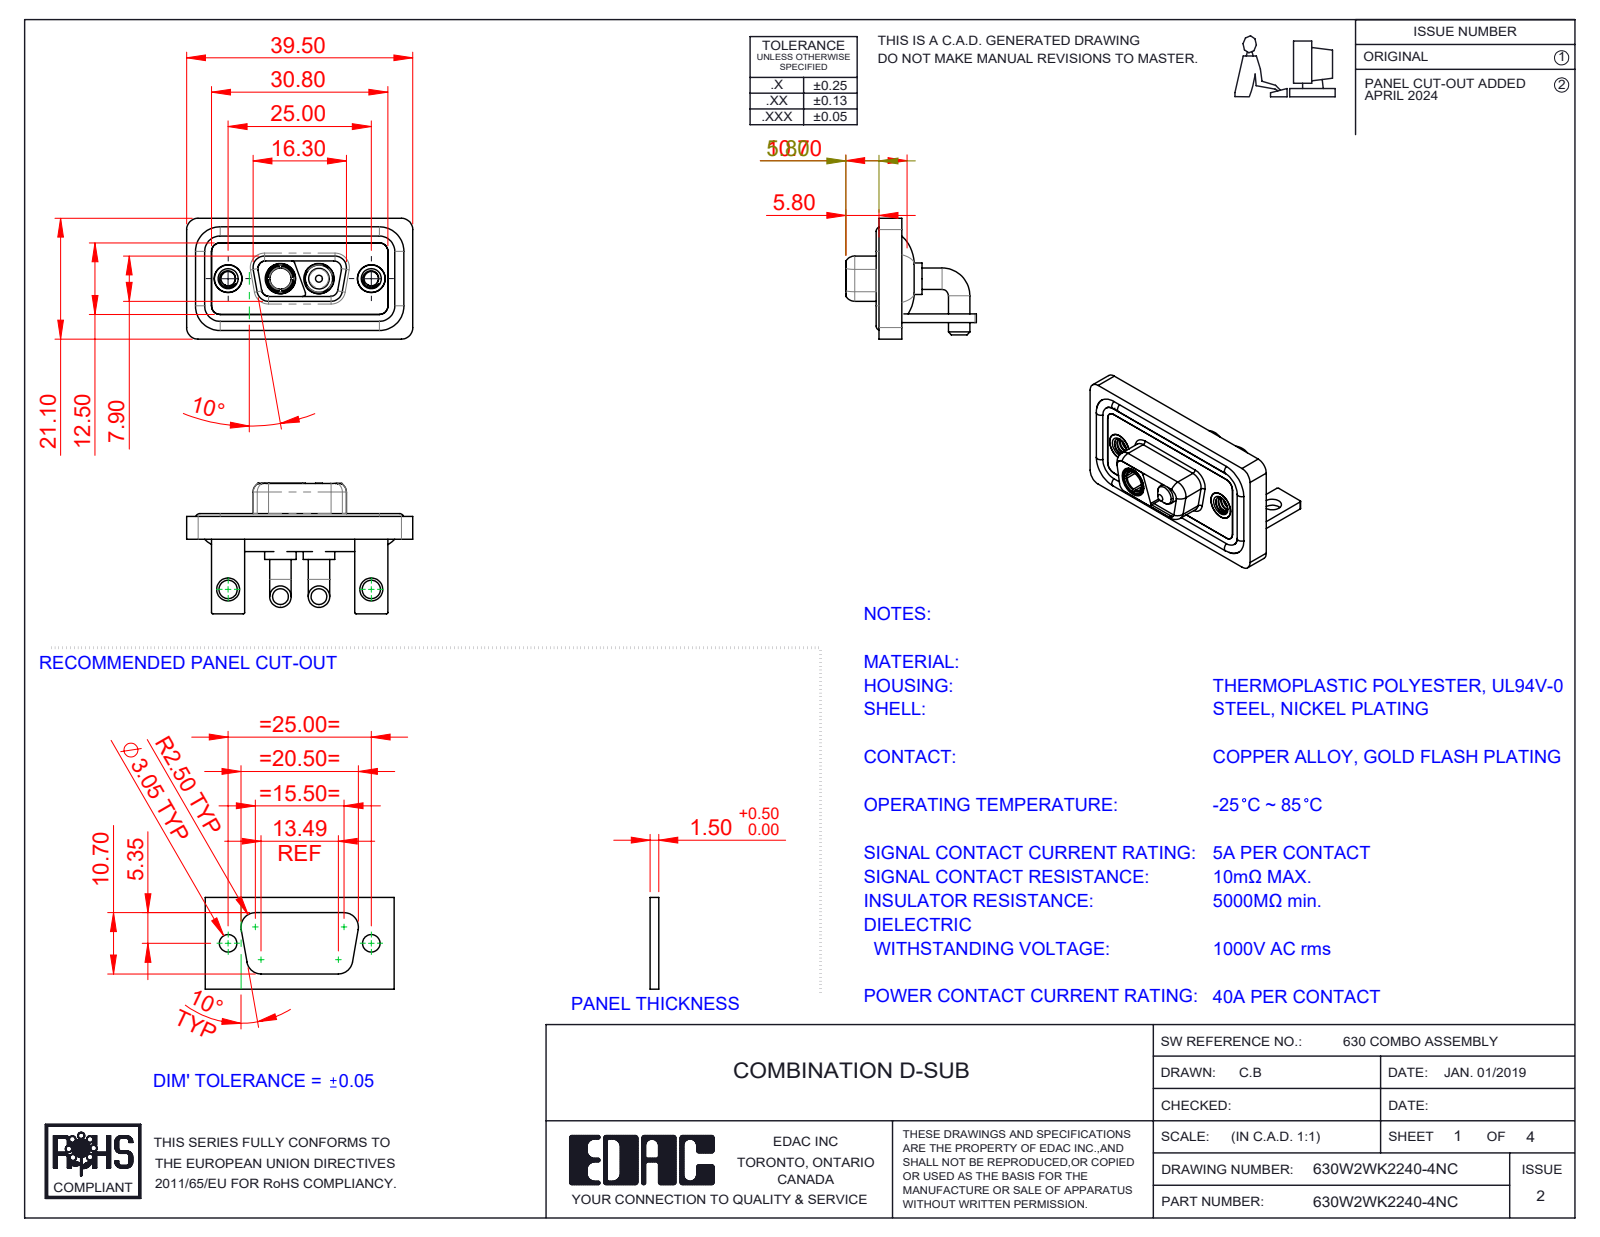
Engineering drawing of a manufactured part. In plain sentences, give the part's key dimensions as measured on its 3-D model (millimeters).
The part is named "Power Pin_40A RA; 630Combo Waterproof Housing_09 Contacts; 630Combo Stabilizer Bracket_50 Contacts; Power Socket_40A RA (+5 more)". Its 3-D file was written by "SolidWorks 2023 (CONFIG_CONTROL_DESIGN)". It is 13 solids with 550 faces: 164 planar, 257 cylindrical and 129 other. Overall it measures 39.5 by 22.8 by 21.1 millimeters. Its volume is 5 212 cubic millimeters and its surface area 8 320 square millimeters. Round holes: 4 of diameter 4.85, 2 of diameter 2.5, 2 of diameter 3.2, 2 of diameter 4, 2 of diameter 4.05, 2 of diameter 5, 2 of diameter 5.3, 1 of diameter 3.7. Round bosses or shafts: 4 of diameter 3.75, 4 of diameter 1.6, 2 of diameter 5.5, 2 of diameter 5.2, 2 of diameter 4.95, 2 of diameter 4.8, 2 of diameter 4.75, 1 of diameter 4.96. Partial cylindrical surfaces (rounded edges, fillets, slot ends): 19 of radius 2, 18 of radius 1.5, 16 of radius 0.25, 8 of radius 1.35, 8 of radius 1.6, 7 of radius 0.5, 4 of radius 0.6, 4 of radius 0.65. The main face-to-face distances are 0.4, 2.9, 1.5, 1.1, 3.7, 1.8, 0.8, 2.5, 1.6, 3.1. The hole center spacings are 9.14, 15.86, 25, 6.72.
